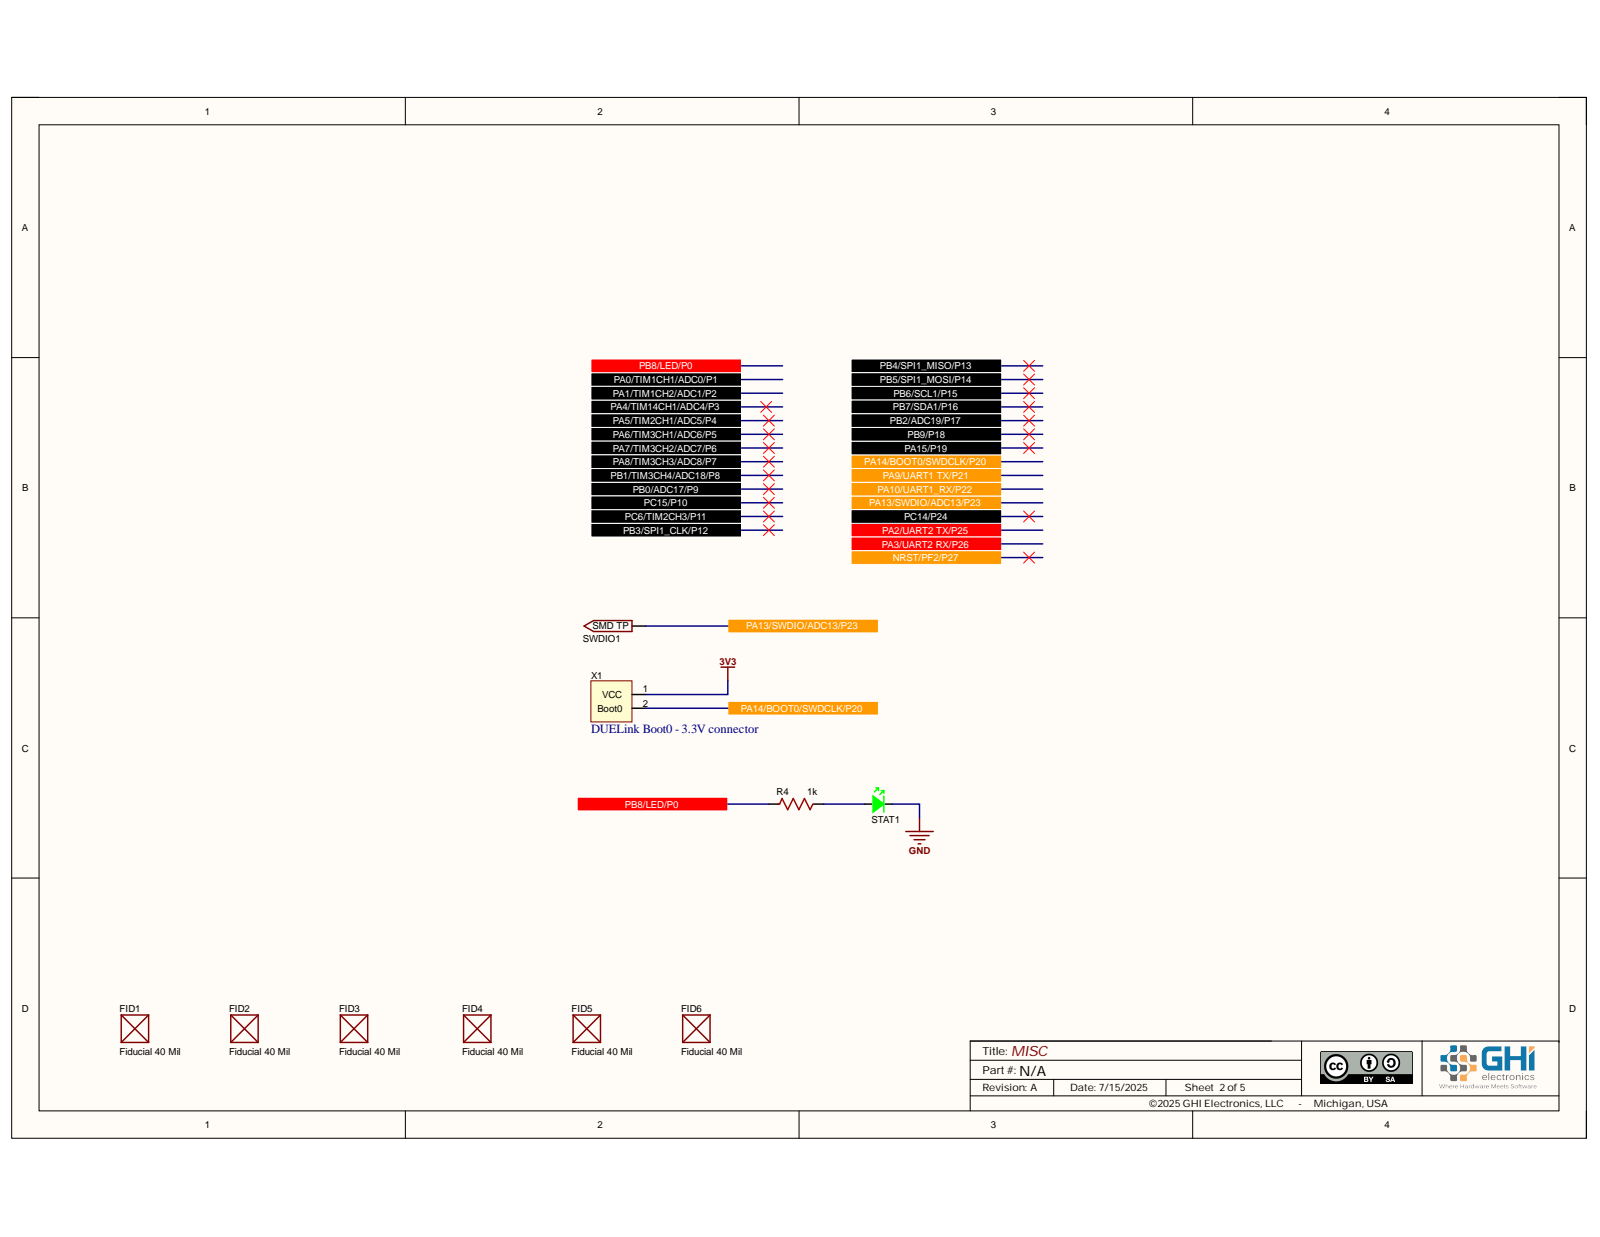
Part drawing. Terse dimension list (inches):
name: PCB; Board; J4; Conn_SAMTEC_TSW-102-07-L-S_eec (+7 more)
written by: Open CASCADE 7.5 (AUTOMOTIVE_DESIGN)
unit: in
bodies: 120 solids, 2764 faces (1437 planar, 717 cylindrical, 610 other)
size: 1.85 × 1.654 × 0.604
volume: 0.278 in³; area: 16.12 in²
holes: 4× ⌀0.118, 2× ⌀0.04, 2× ⌀0.04, 1× ⌀0.787, 1× ⌀0.906, 1× ⌀0.926, 1× ⌀0.993, 1× ⌀1.024
bosses: 4× ⌀0.039, 1× ⌀0.978, 1× ⌀0.911, 1× ⌀0.852, 1× ⌀0.63
rounds: 35× R0.005, 26× R0.006, 4× R0.138, 2× R0.007, 2× R0.007, 2× R0.007, 1× R0.004
face distances: 0.039, 0.079, 0.315, 0.118, 0.047, 0.197, 0.472, 0.276, 0.236, 0.425
hole spacings: 1.046, 0.1, 1.378, 1.575, 1.661, 2.093, 0.554, 0.561
